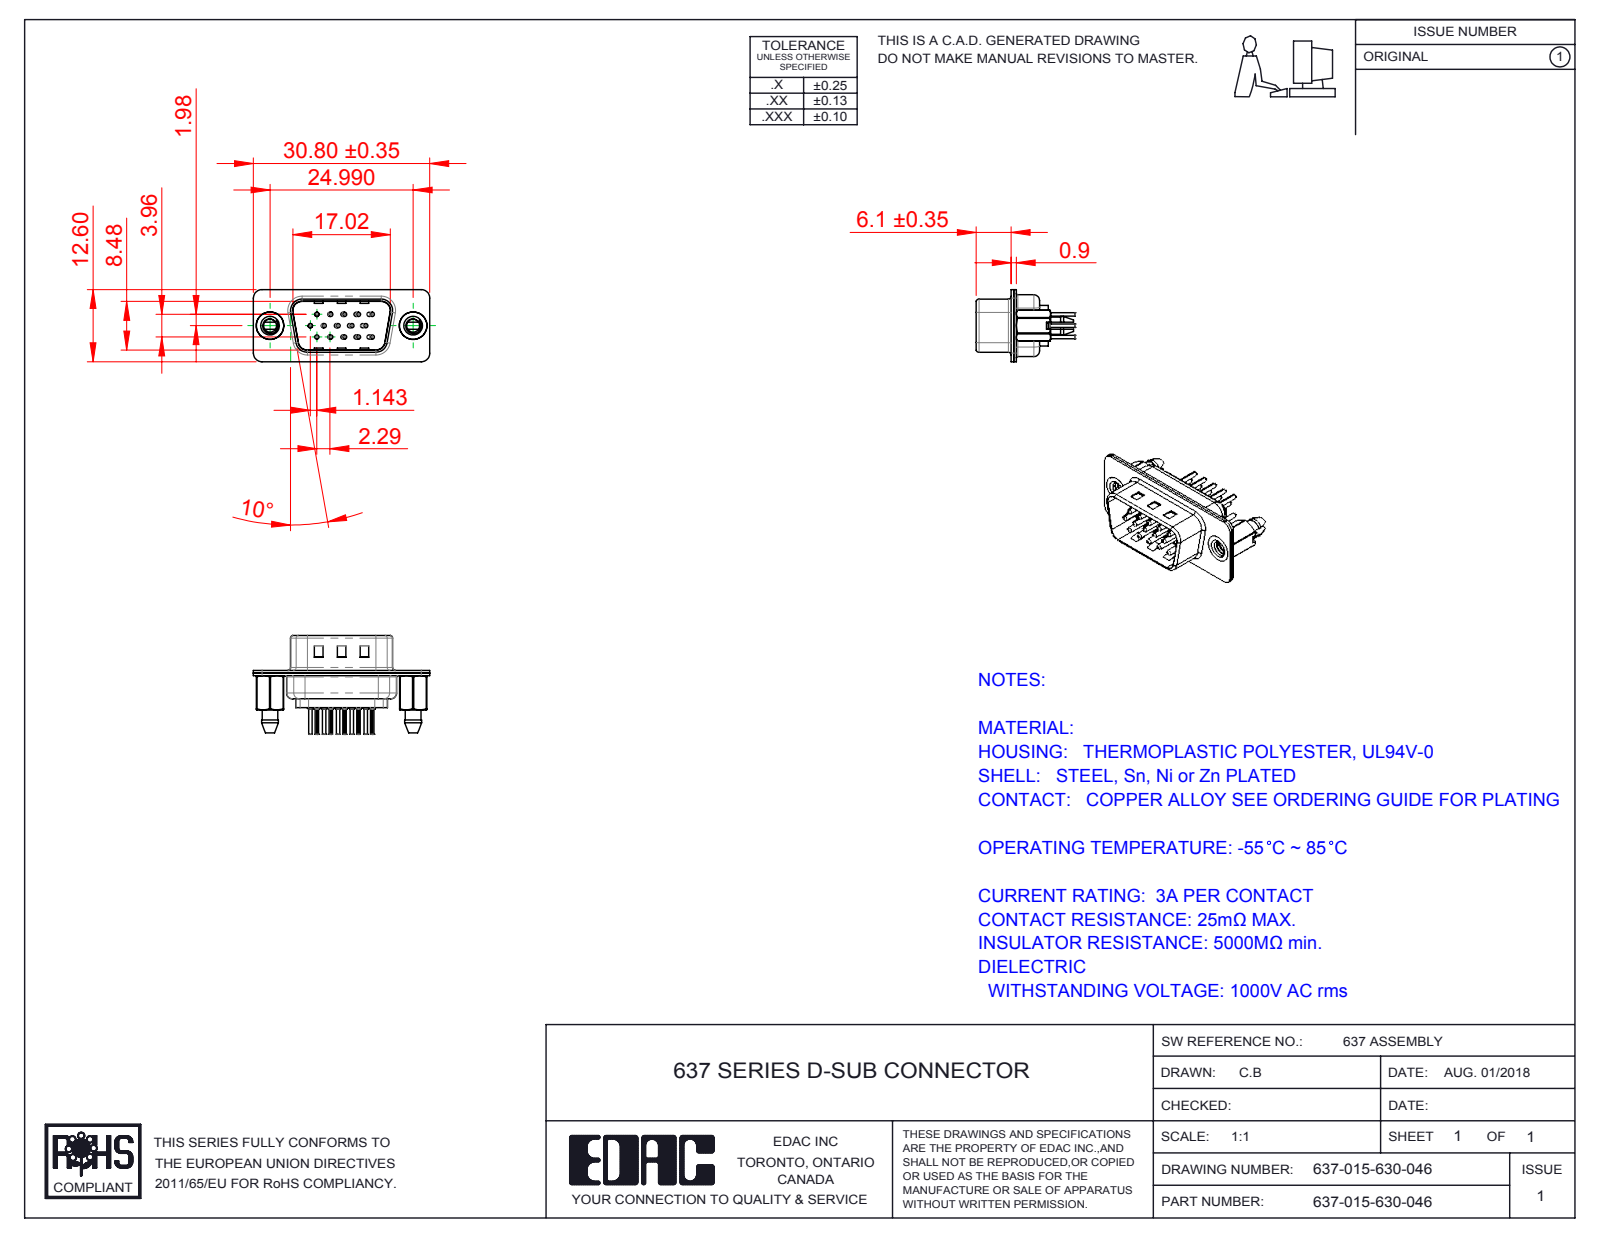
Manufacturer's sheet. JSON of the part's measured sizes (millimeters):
{"part_name": "637-015-630-046; 637 4-40 Threaded Boardlock_LP; 637 Contact Row 3_30; 637 Contact Row 2_30 (+4 more)", "step_written_by": "SolidWorks 2016 (CONFIG_CONTROL_DESIGN)", "units": "millimeters", "bodies": {"solids": 20, "faces": 1878, "planar": 499, "cylindrical": 716, "other": 663}, "overall_size": [30.8, 17.25, 12.6], "volume_mm3": 1429, "surface_area_mm2": 4933, "round_holes": [[1.6, 27], [0.2, 15], [0.35, 15], [1.1, 15], [0.75, 12], [2, 12], [2.26, 2], [4, 2], [4.8, 2]], "round_bosses_or_shafts": [[2, 15], [1.5, 15], [0.75, 15], [0.6, 15], [4.9, 2]], "partial_cylinders_radius": [[0.1, 30], [1.5, 18], [2, 12], [0.5, 8], [1.6, 6], [0.25, 4], [0.55, 4], [0.7, 4]], "face_to_face_distances": [0.45, 0.4, 0.9, 8.48, 0.7, 8.88, 6.5, 4.55, 0.31, 1.05], "hole_center_spacings": [3.96, 2.29, 2.28, 4.57, 2.42, 6.05, 4.84, 2.35]}
